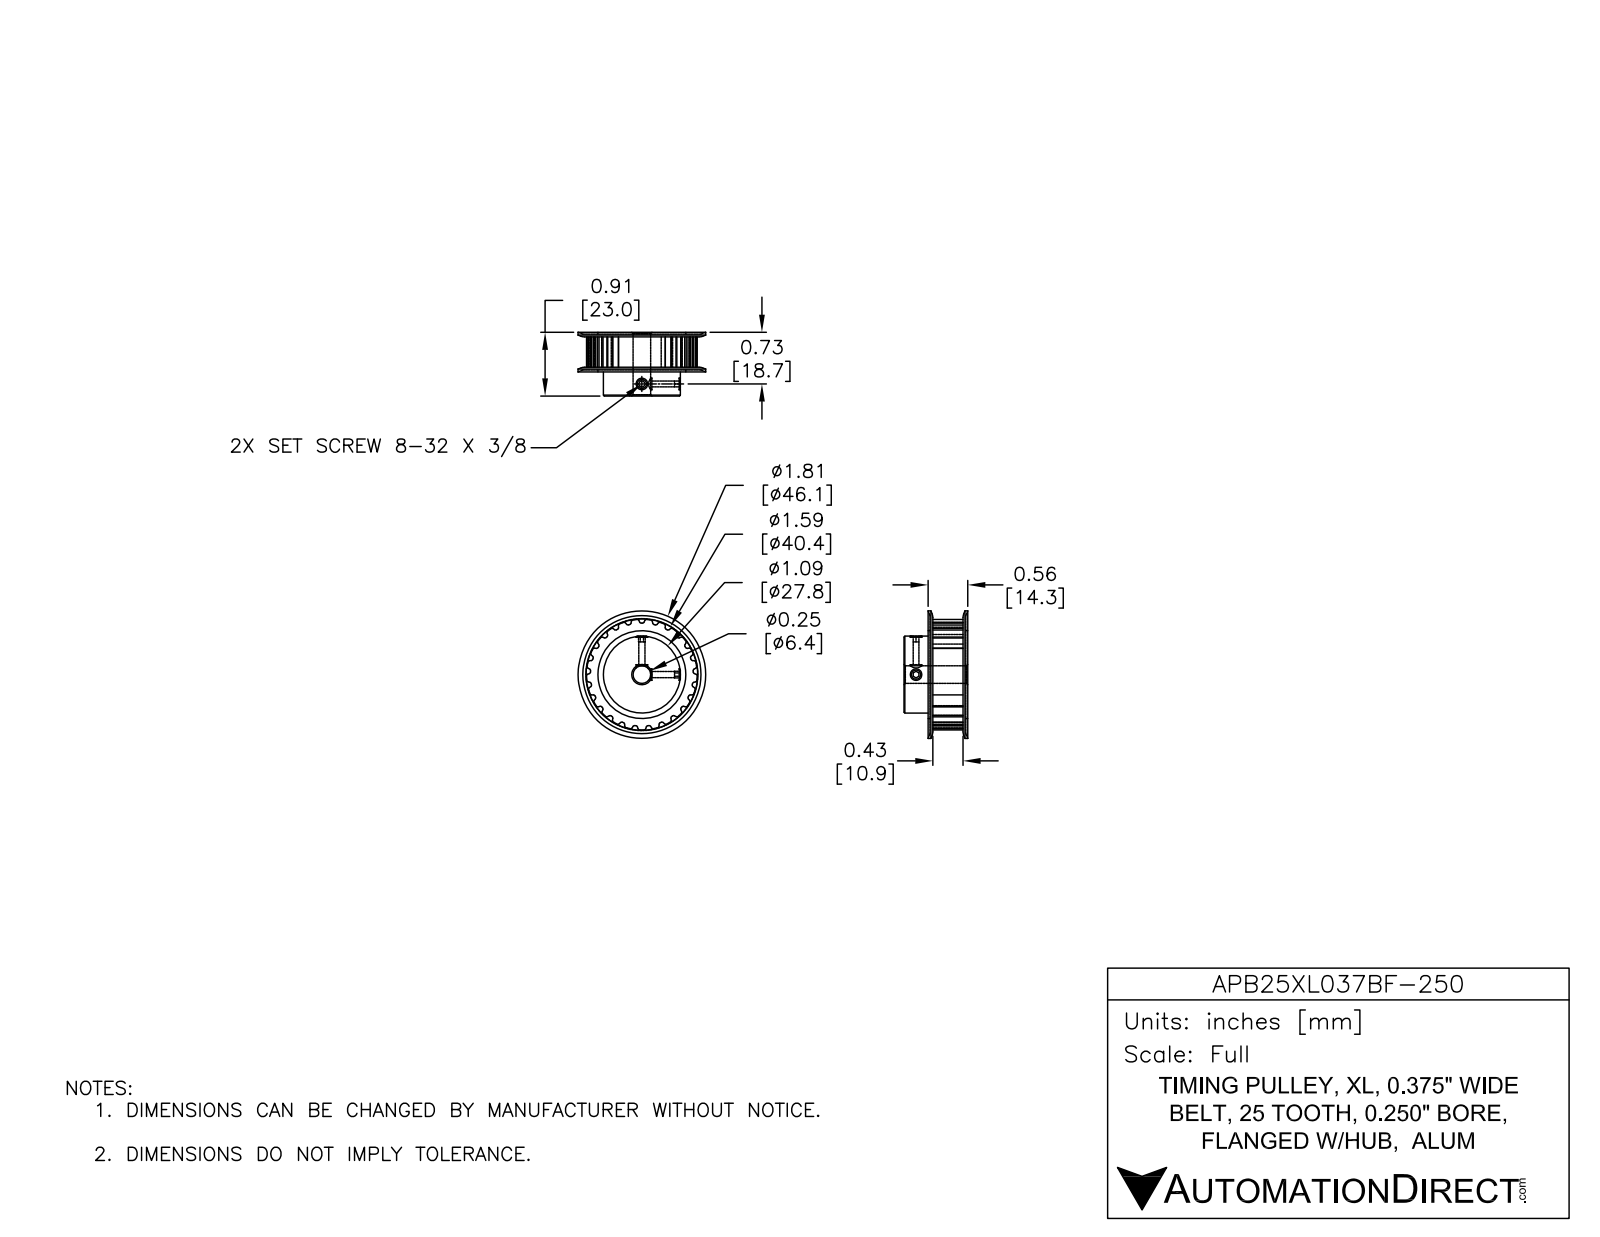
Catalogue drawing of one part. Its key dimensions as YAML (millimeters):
part_name: "APB25XL037BF-250"
step_written_by: "SolidWorks 2014 (AUTOMOTIVE_DESIGN)"
units: millimeters
bodies: {solids: 1, faces: 257, planar: 81, cylindrical: 154, other: 22}
overall_size: [46.05, 46.05, 23.01]
volume: 21206
surface_area: 7715
round_holes:
  - {diameter: 2.23, count: 2}
  - {diameter: 6.35, count: 1}
round_bosses_or_shafts:
  - {diameter: 27.79, count: 1}
partial_cylinders:
  - {radius: 0.38, count: 100}
  - {radius: 18.57, count: 1}
face_to_face_distances: [12.57, 0.83, 13.4, 23.01, 22.18, 9.61, 11.74, 10.44, 1.65, 0.82]
